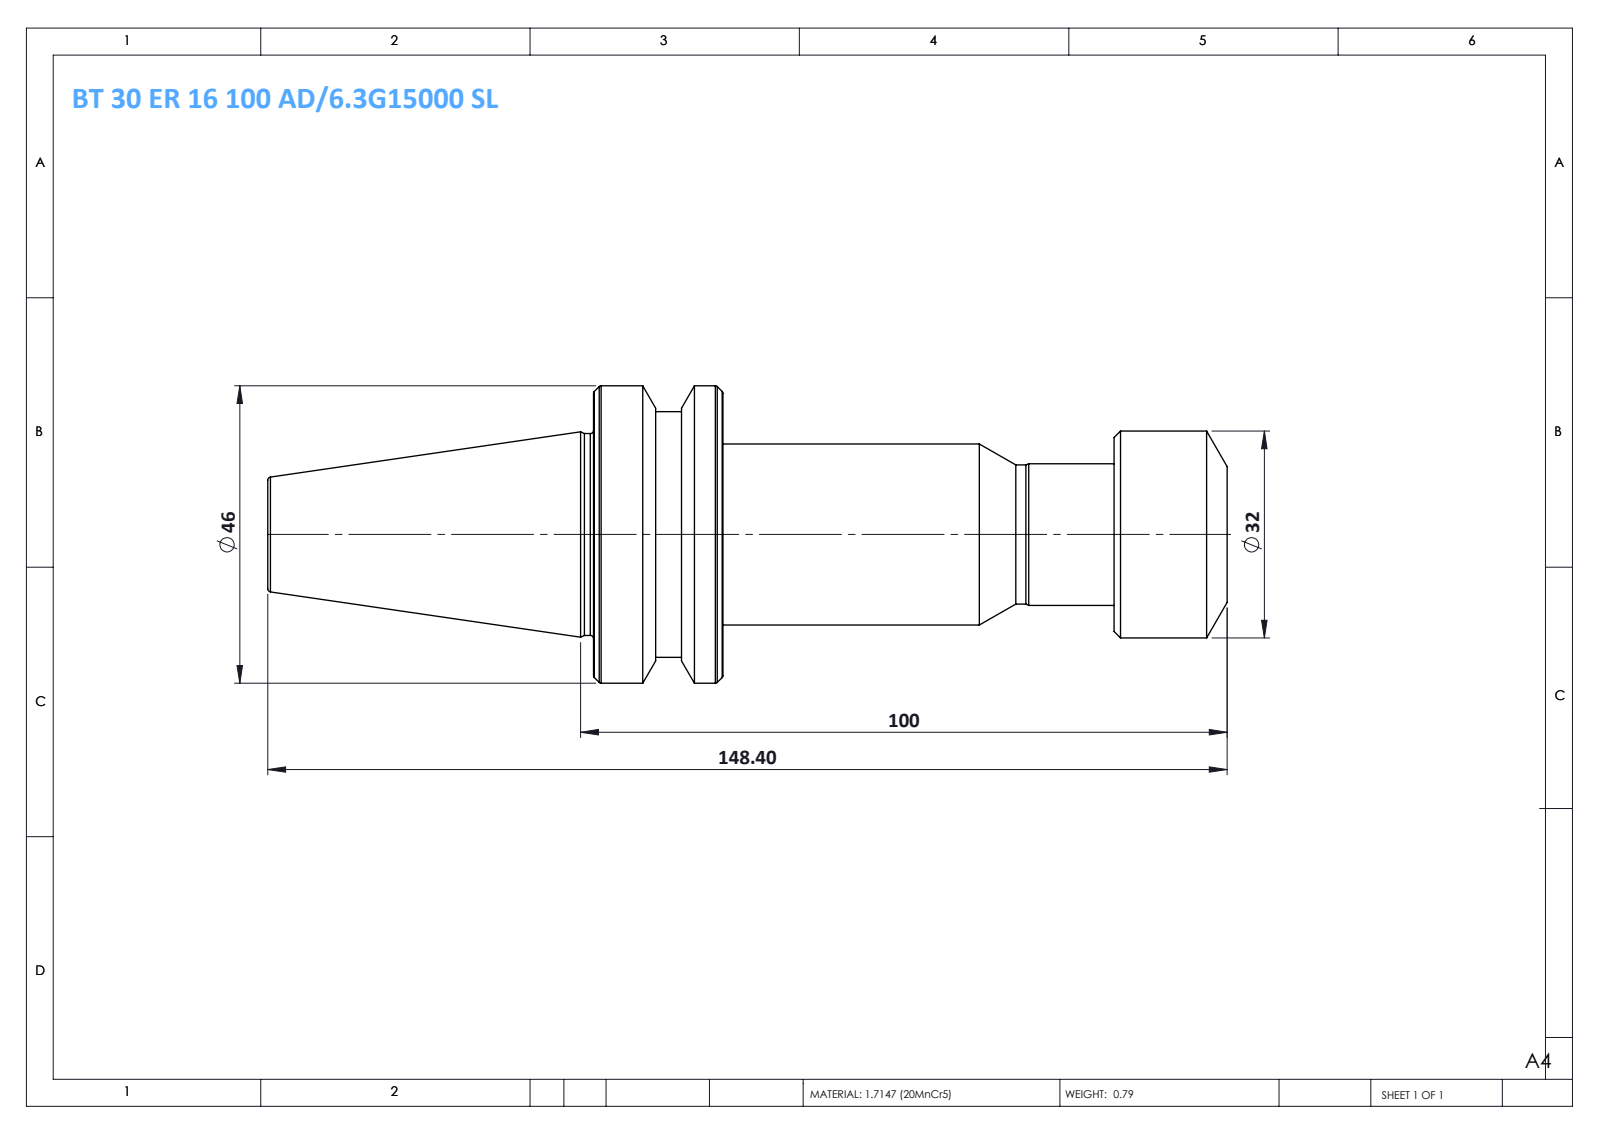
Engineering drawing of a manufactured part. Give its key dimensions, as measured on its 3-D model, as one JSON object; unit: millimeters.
{"part_name": "BT 30 ER 16 100 AD-6.3G15000 SL", "step_written_by": "SolidWorks 2014 (CONFIG_CONTROL_DESIGN)", "units": "millimeters", "bodies": {"solids": 1, "faces": 55, "planar": 7, "cylindrical": 16, "other": 32}, "overall_size": [148.4, 46, 46], "volume_mm3": 101479, "surface_area_mm2": 17108, "round_bosses_or_shafts": [[46, 1], [38, 1], [32, 1], [31.2, 1], [28, 1], [21.9, 1], [21.5, 1]], "face_to_face_distances": [20, 78, 98, 17.5, 60.5, 80.5, 148.4, 130.9, 70.4, 50.4]}
